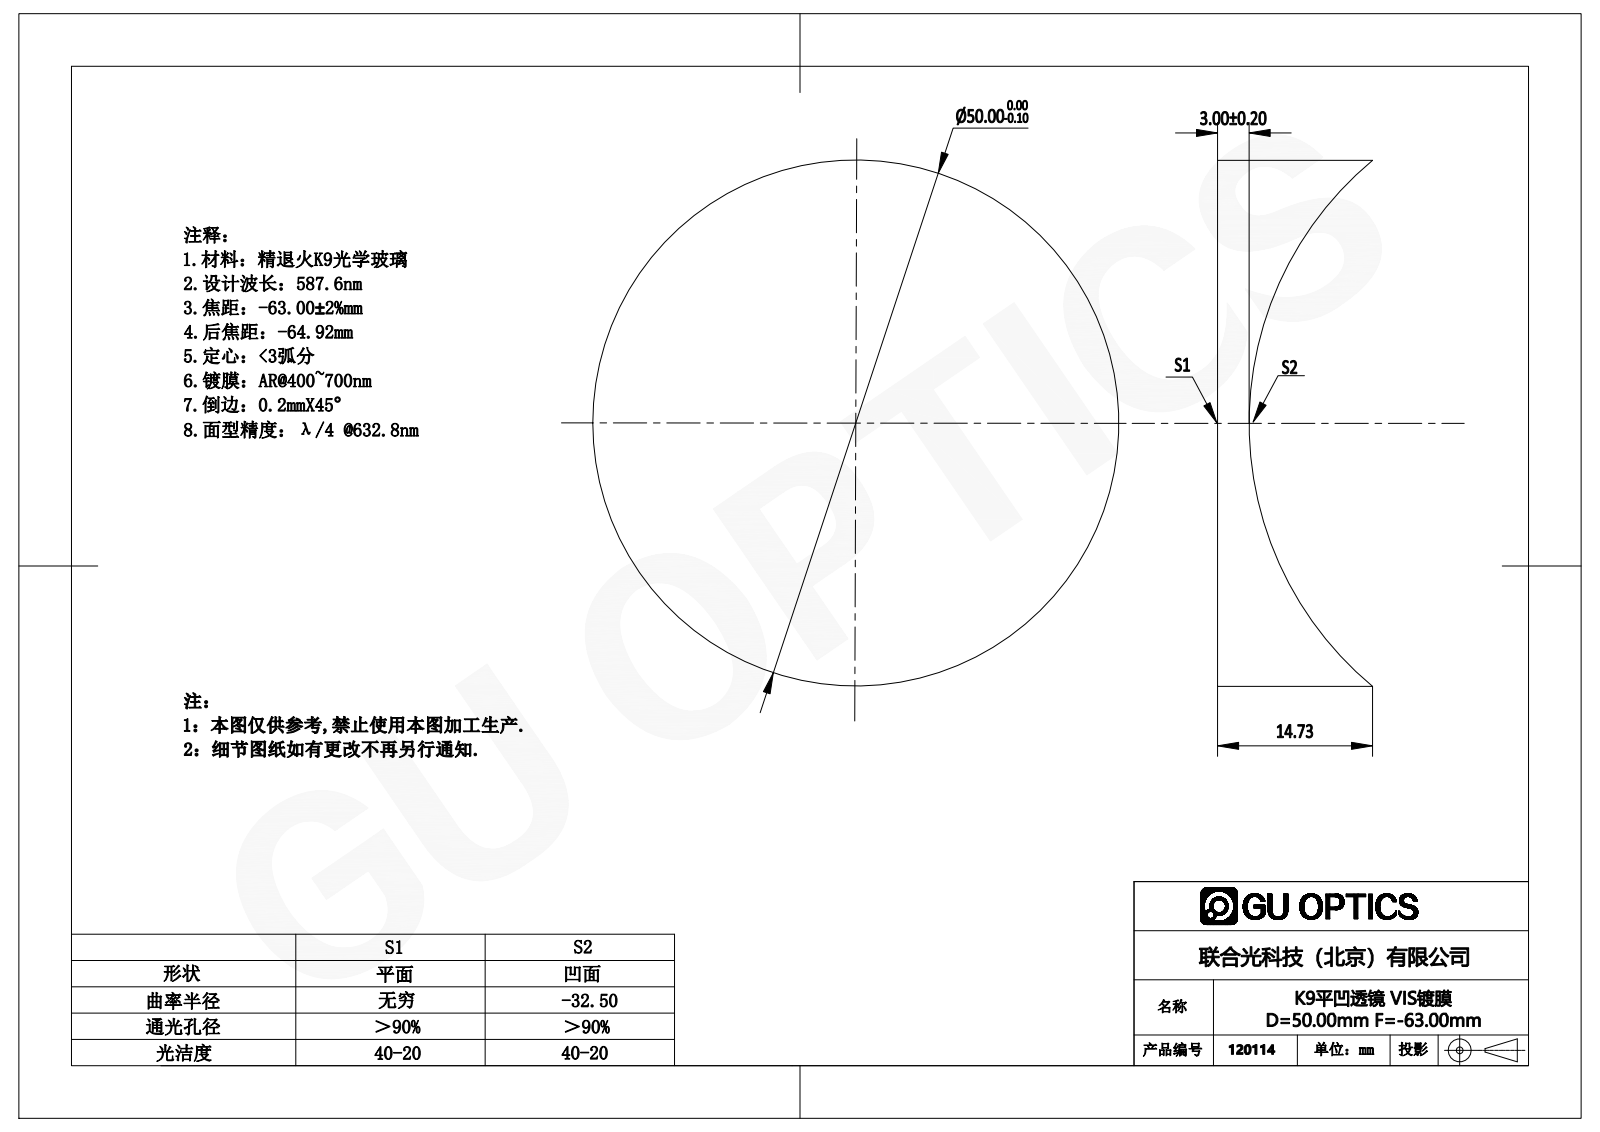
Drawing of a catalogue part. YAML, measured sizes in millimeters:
part_name: "120054"
step_written_by: "SolidWorks 2016 (AUTOMOTIVE_DESIGN)"
units: millimeters
bodies: {solids: 1, faces: 5, planar: 1, cylindrical: 2, other: 2}
overall_size: [50, 50, 14.73]
volume: 16564
surface_area: 6674
round_bosses_or_shafts:
  - {diameter: 50, count: 1}
